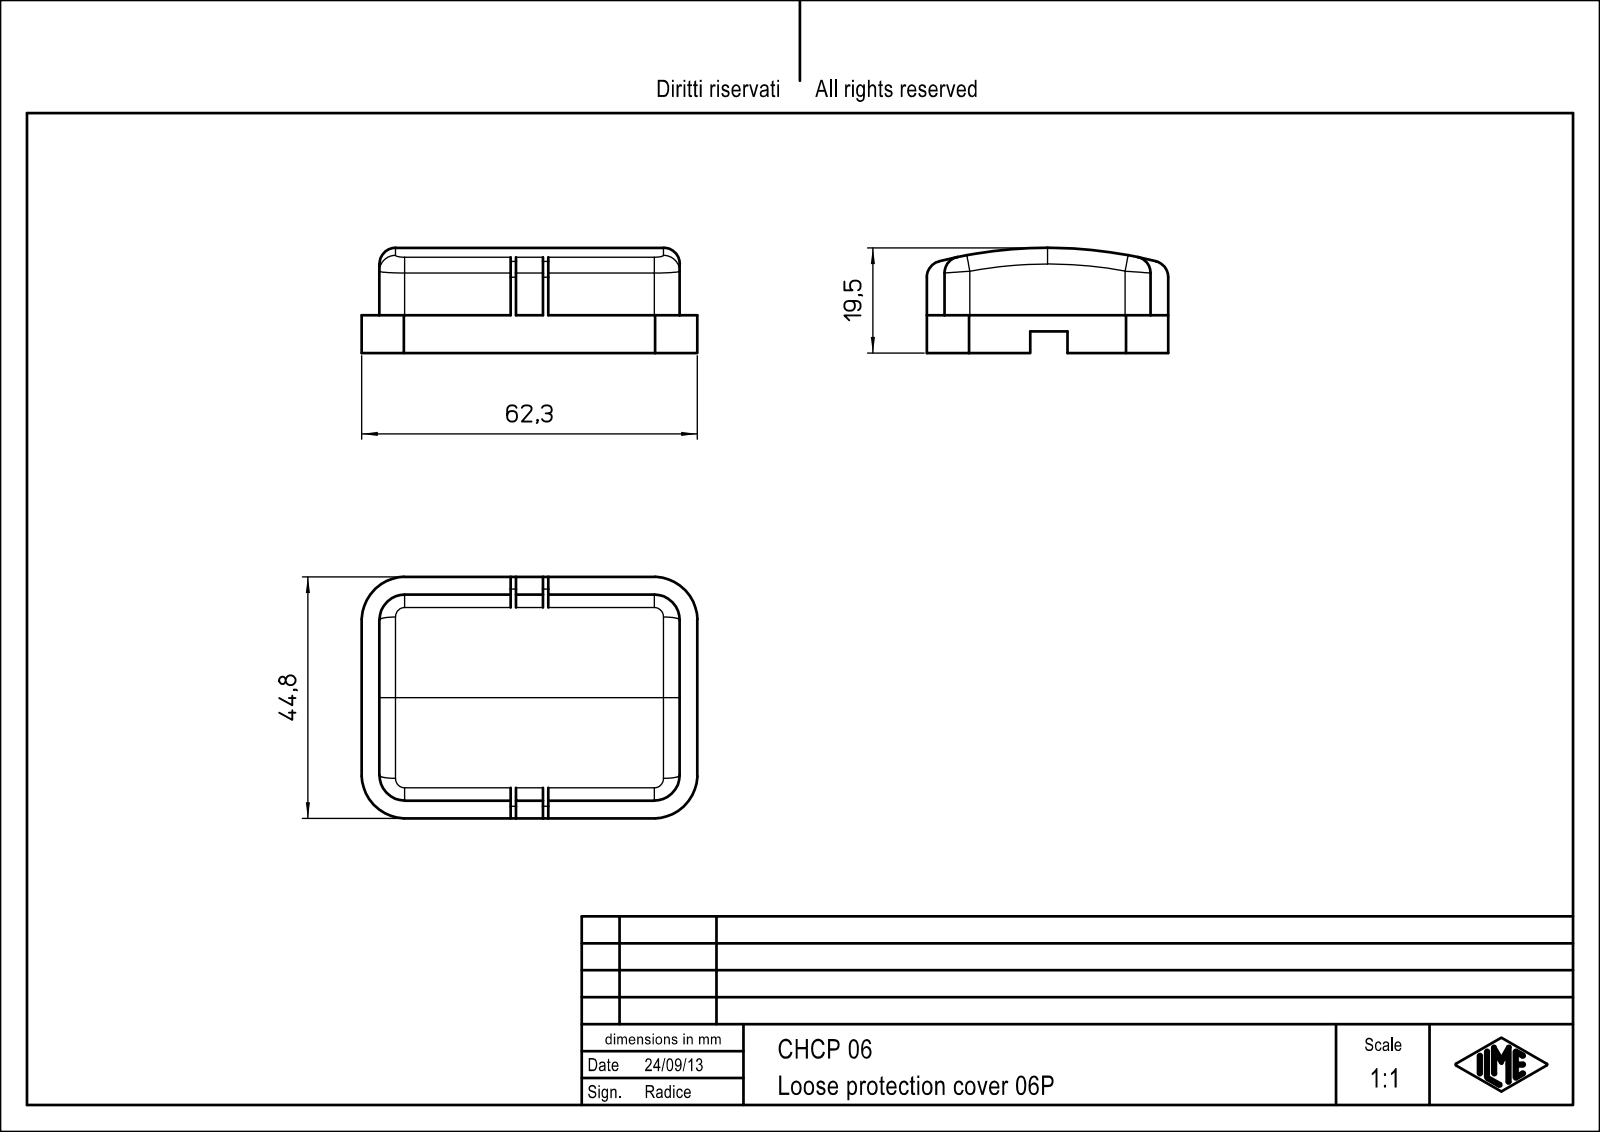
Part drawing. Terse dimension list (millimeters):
name: CHCP_06
written by: Creo Elements/Direct Modeling 18.0B 02-Dec-2011 (C) Parametric Technology GmbH (AUTOMOTIVE_DESIGN)
unit: mm
bodies: 1 solid, 145 faces (72 planar, 56 cylindrical, 17 other)
size: 62.3 × 44.8 × 19.5
volume: 5 903 mm³; area: 11 868 mm²
rounds: 15× R0.33, 8× R3, 4× R4.7, 4× R7.2, 4× R8.11, 2× R0.17, 2× R81, 2× R82
face distances: 4.4, 1.12, 3.28, 0.9, 3.5, 1, 2.38, 37.12, 40.4, 41.52
